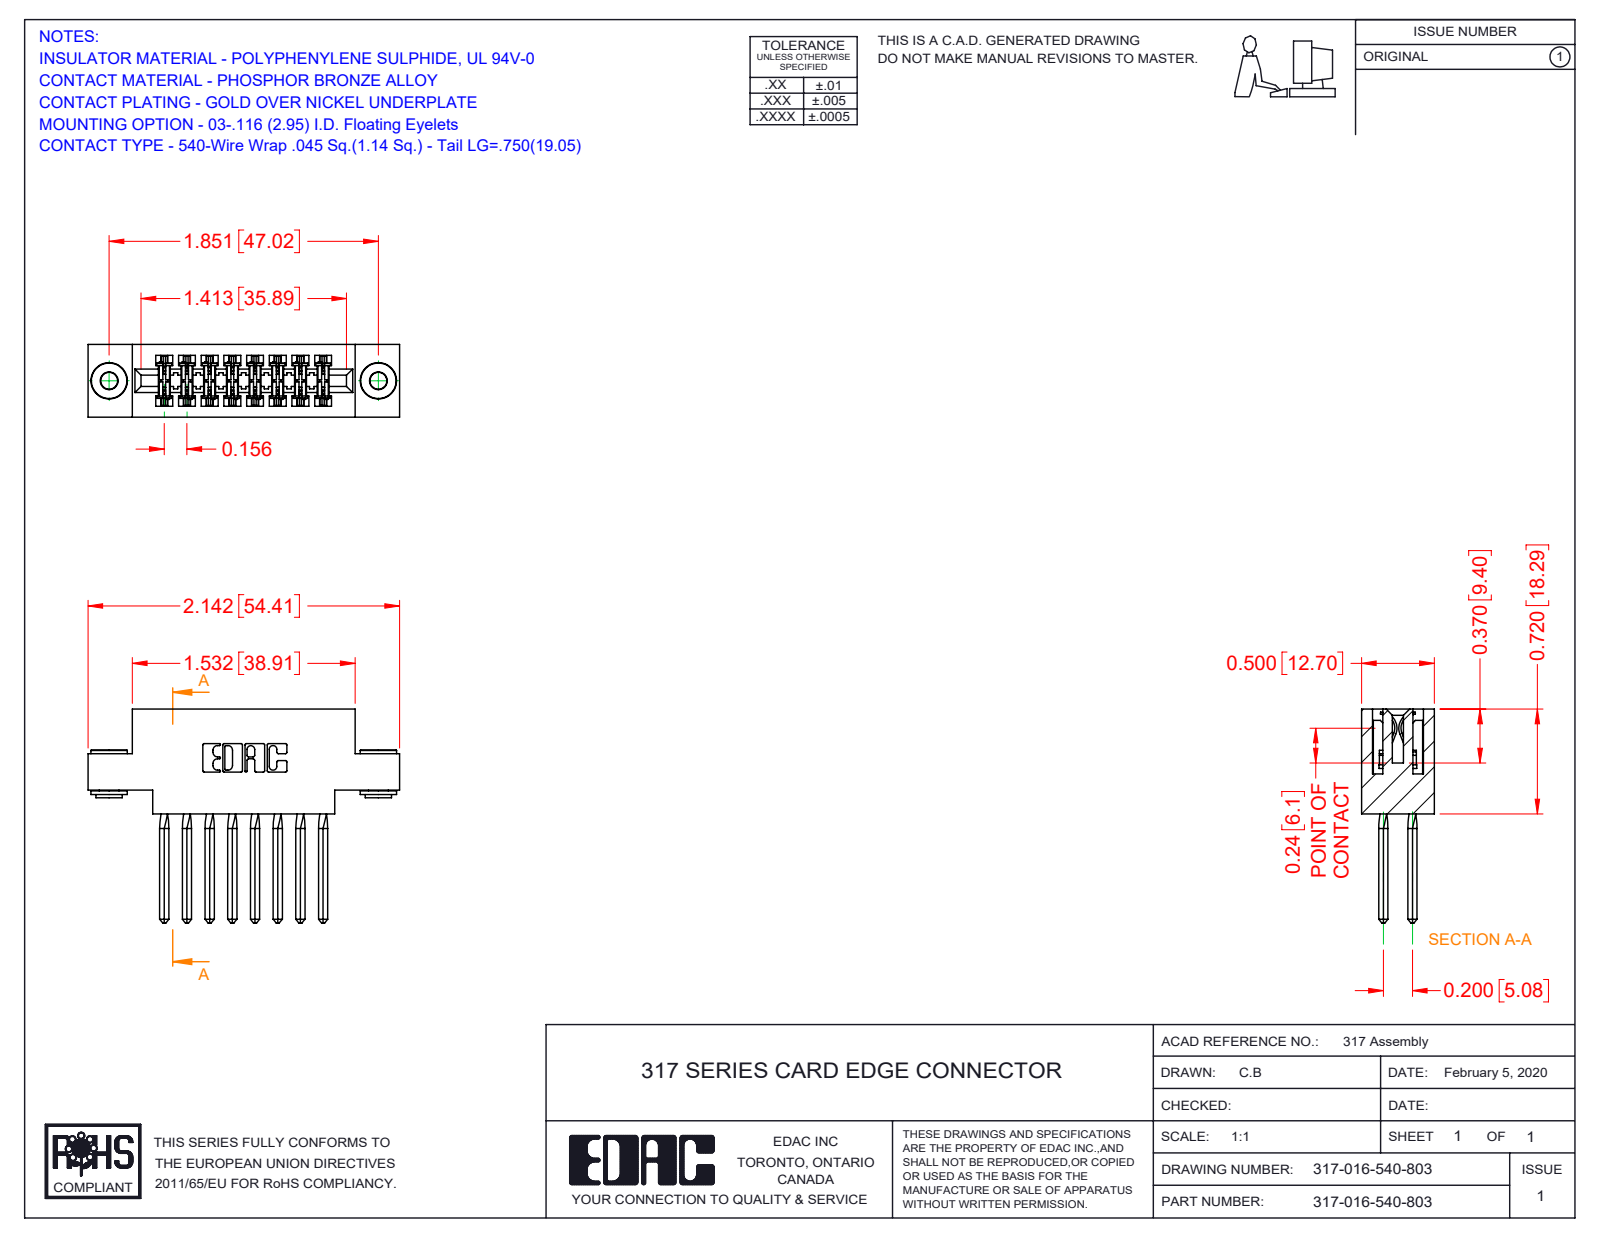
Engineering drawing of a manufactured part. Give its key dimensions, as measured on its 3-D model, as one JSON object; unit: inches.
{"part_name": "317-016-540-803; 345-250-002_345-250-002-102; 317-290-001_540; 317 Part_.156 Dia - TH", "step_written_by": "SolidWorks 2016 (CONFIG_CONTROL_DESIGN)", "units": "inches", "bodies": {"solids": 19, "faces": 1564, "planar": 1236, "cylindrical": 256, "other": 72}, "overall_size": [2.142, 1.47, 0.5], "volume_in3": 0.488, "surface_area_in2": 16.83, "round_holes": [[0.116, 2], [0.156, 2]], "round_bosses_or_shafts": [[0.25, 2], [0.18, 2], [0.136, 2]], "partial_cylinders_radius": [[0.015, 32], [0.01, 22], [0.007, 6], [0.031, 6], [0.026, 3], [0.095, 2], [0.1, 2], [0.11, 2]], "face_to_face_distances": [0.5, 0.075, 0.11, 0.425, 0.22, 0.156, 0.116, 0.305, 0.35, 0.163], "hole_center_spacings": [1.851]}
